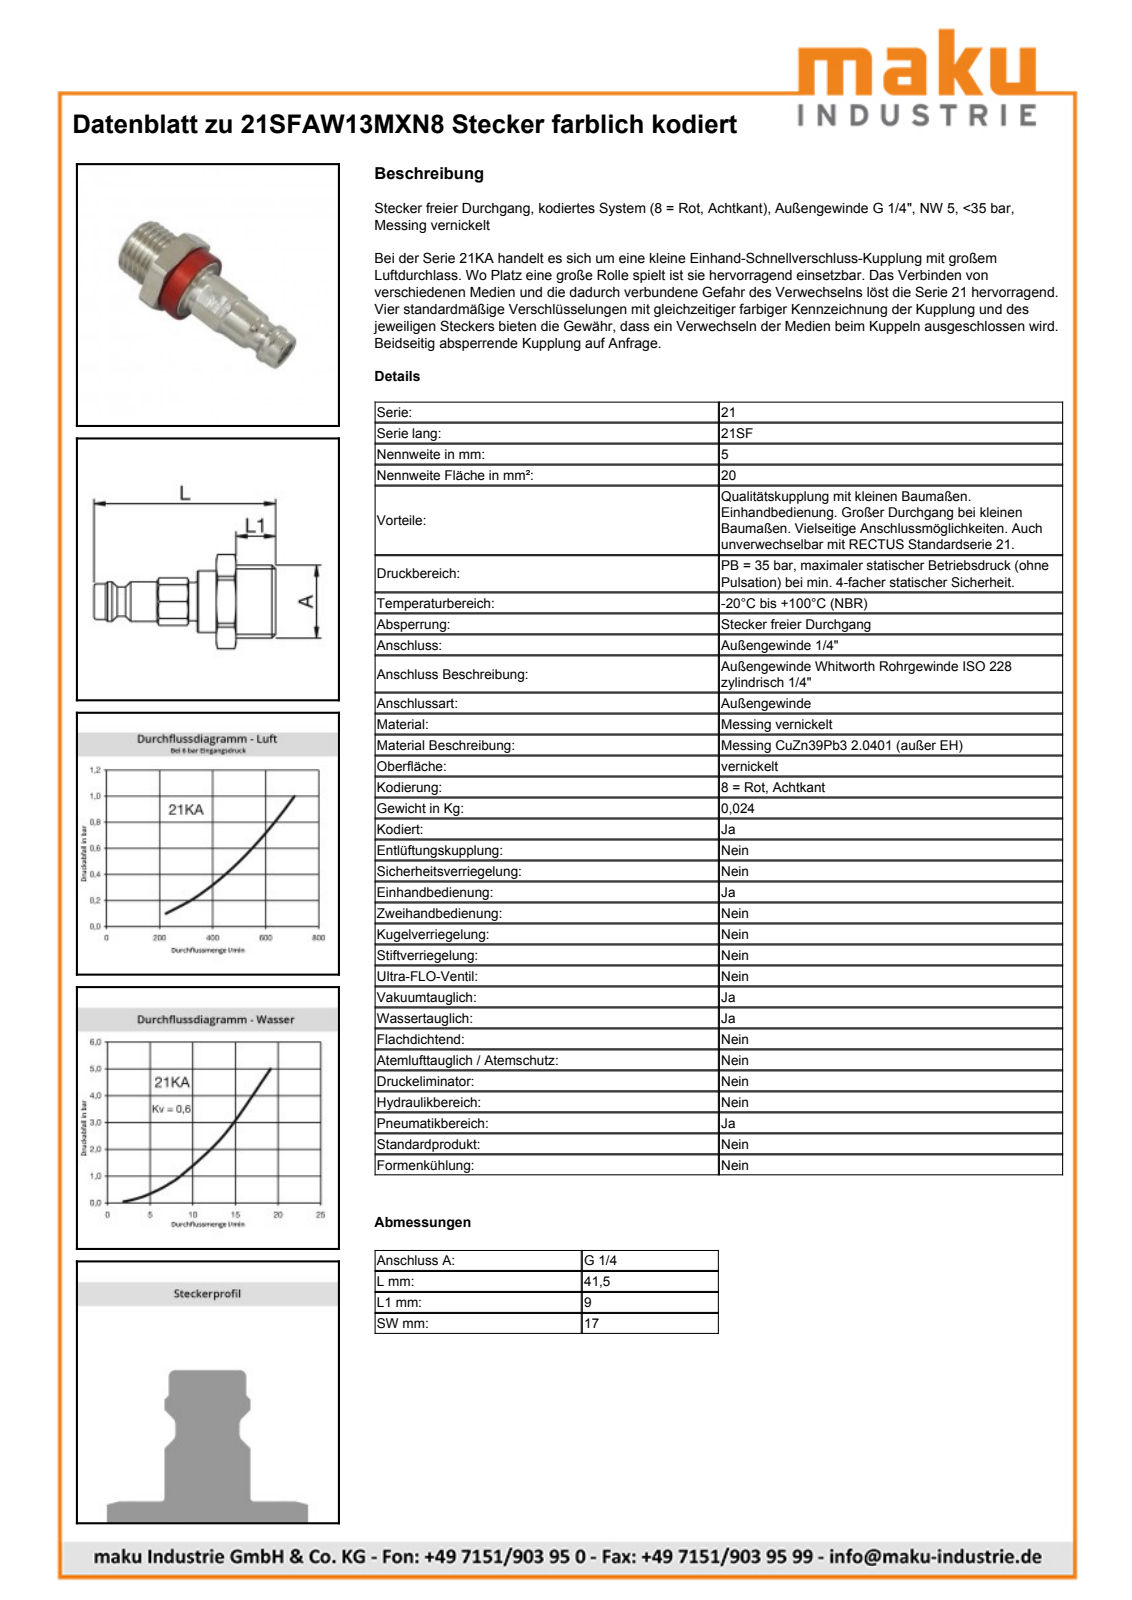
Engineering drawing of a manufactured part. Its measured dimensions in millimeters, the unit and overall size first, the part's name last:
Units: millimetres
Overall size (bounding box): 41.5 × 19 × 17
Round holes (diameter × count): ⌀4.95 ×1, ⌀13.85 ×1, ⌀14.05 ×1
Round bosses / shafts (diameter × count): ⌀15.5 ×1, ⌀14 ×1, ⌀13.16 ×1, ⌀9.7 ×1, ⌀9 ×1, ⌀8.1 ×1, ⌀6.65 ×1
Partial cylindrical surfaces — rounded edges, fillets, slot ends (radius × count): R5.35 ×1, R9.5 ×1
Main face-to-face distances: 4.5, 17, 10, 9, 13.5, 3.5, 18, 4.2, 8.7, 17.7
Volume: 3 765 mm³ · Surface area: 3 016 mm²
Bodies: 2 solids, 73 faces (21 planar, 25 cylindrical, 27 other)
Part name (STEP PRODUCT): D103778; D103772; D103012
STEP written by: Autodesk Inventor 2011 (AUTOMOTIVE_DESIGN)
